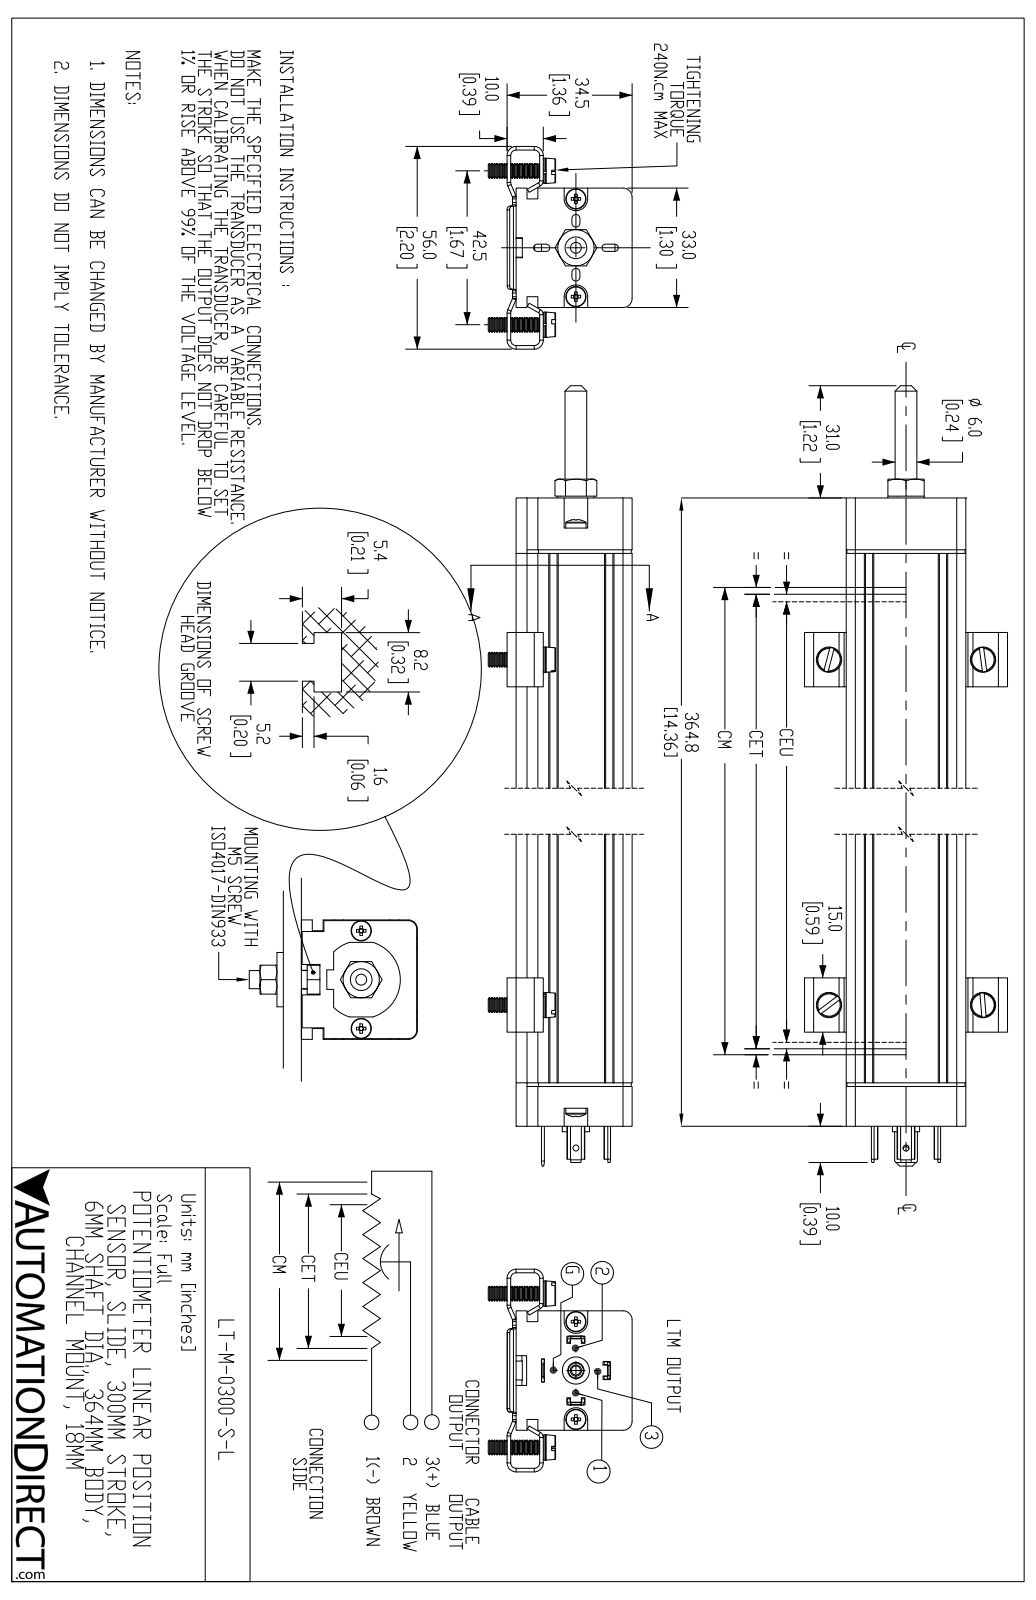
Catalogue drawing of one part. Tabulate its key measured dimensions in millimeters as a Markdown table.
| quantity | value |
| --- | --- |
| part name | LT-M-0300-S-L |
| STEP written by | SolidWorks 2019 (AUTOMOTIVE_DESIGN) |
| units | millimeters |
| bodies | 21 solids, 1620 faces (696 planar, 356 cylindrical, 568 other) |
| overall size | 424.4 × 56 × 39.7 |
| volume | 370 800 mm³ |
| surface area | 86 390 mm² |
| round holes (diameter × count) | 3.6 × 4, 1.5 × 2, 1.7 × 2, 2.7 × 2, 3.4 × 2, 4.3 × 2, 1.6 × 1, 2.5 × 1, 3 × 1, 4.1 × 1, 5 × 1, 7 × 1 |
| round bosses / shafts (diameter × count) | 7 × 4, 4 × 4, 5.6 × 2, 3 × 2, 7.5 × 1, 6 × 1, 4.5 × 1, 4.4 × 1 |
| partial cylindrical surfaces (radius × count) | 1 × 34, 2.5 × 12, 1.5 × 10, 2.2 × 8, 0.8 × 6, 1.1 × 4, 0.6 × 2, 1.6 × 2 |
| main face-to-face distances | 32, 33, 3, 32.7, 5.4, 1, 26.6, 12.4, 20.3, 20.6 |
| hole center spacings | 12.3, 13.5, 34.5, 42.2, 42.5, 44.9, 45.2, 297.8 |
